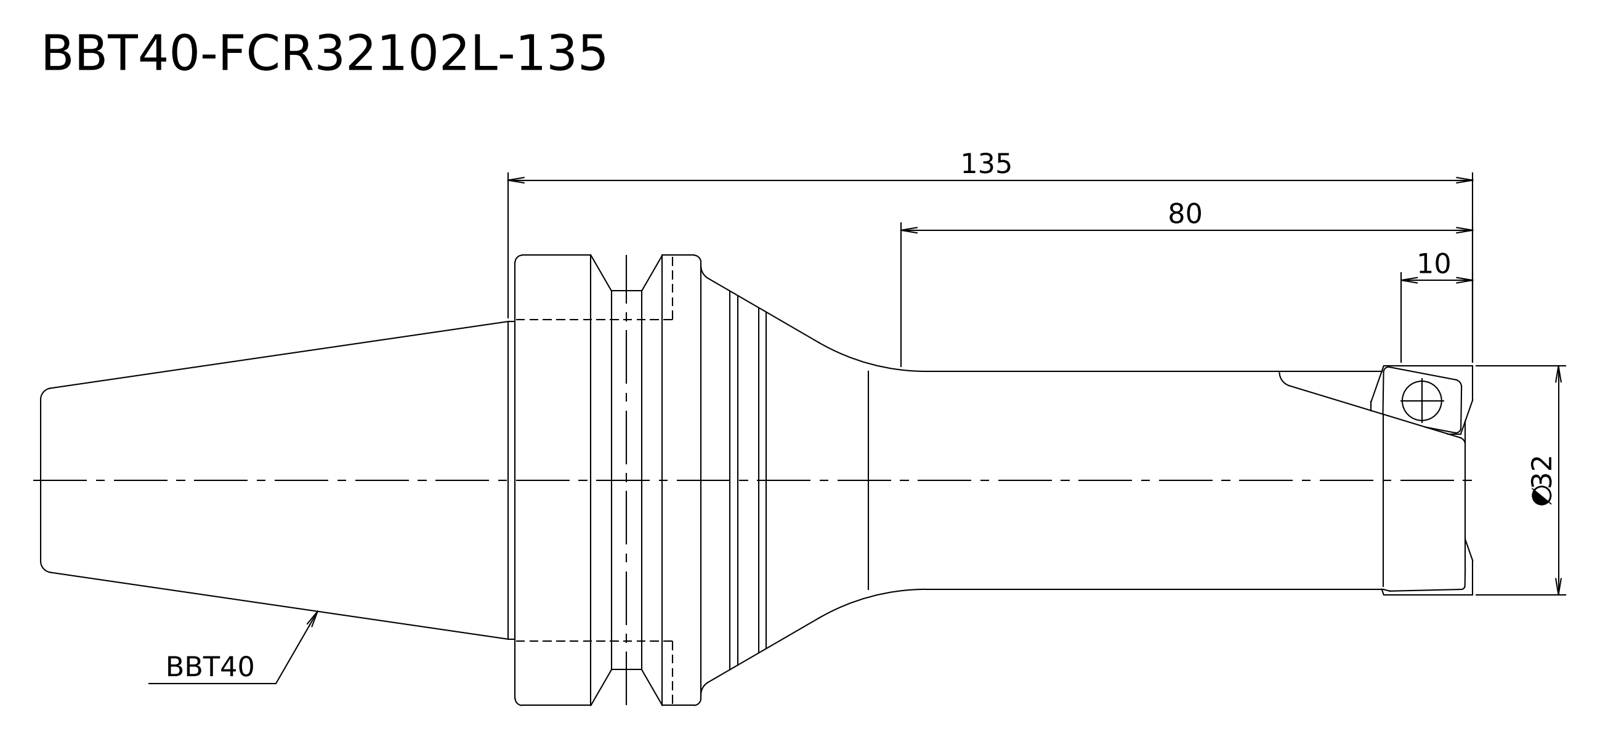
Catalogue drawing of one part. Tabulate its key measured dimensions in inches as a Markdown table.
| quantity | value |
| --- | --- |
| STEP written by | Kubotek KeyCreator V8.5.1 (14335) (CONFIG_CONTROL_DESIGN) |
| units | inches |
| bodies | 1 solid, 17 faces (4 planar, 6 cylindrical, 7 other) |
| overall size | 7.89 × 2.48 × 2.48 |
| volume | 14.74 in³ |
| surface area | 44.41 in² |
| round bosses / shafts (diameter × count) | 2.48 × 1, 2.087 × 1, 1.75 × 1, 1.26 × 1, 1.201 × 1 |
| main face-to-face distances | 5.276, 7.89, 2.614, 4.252, 1.024, 3.638 |
